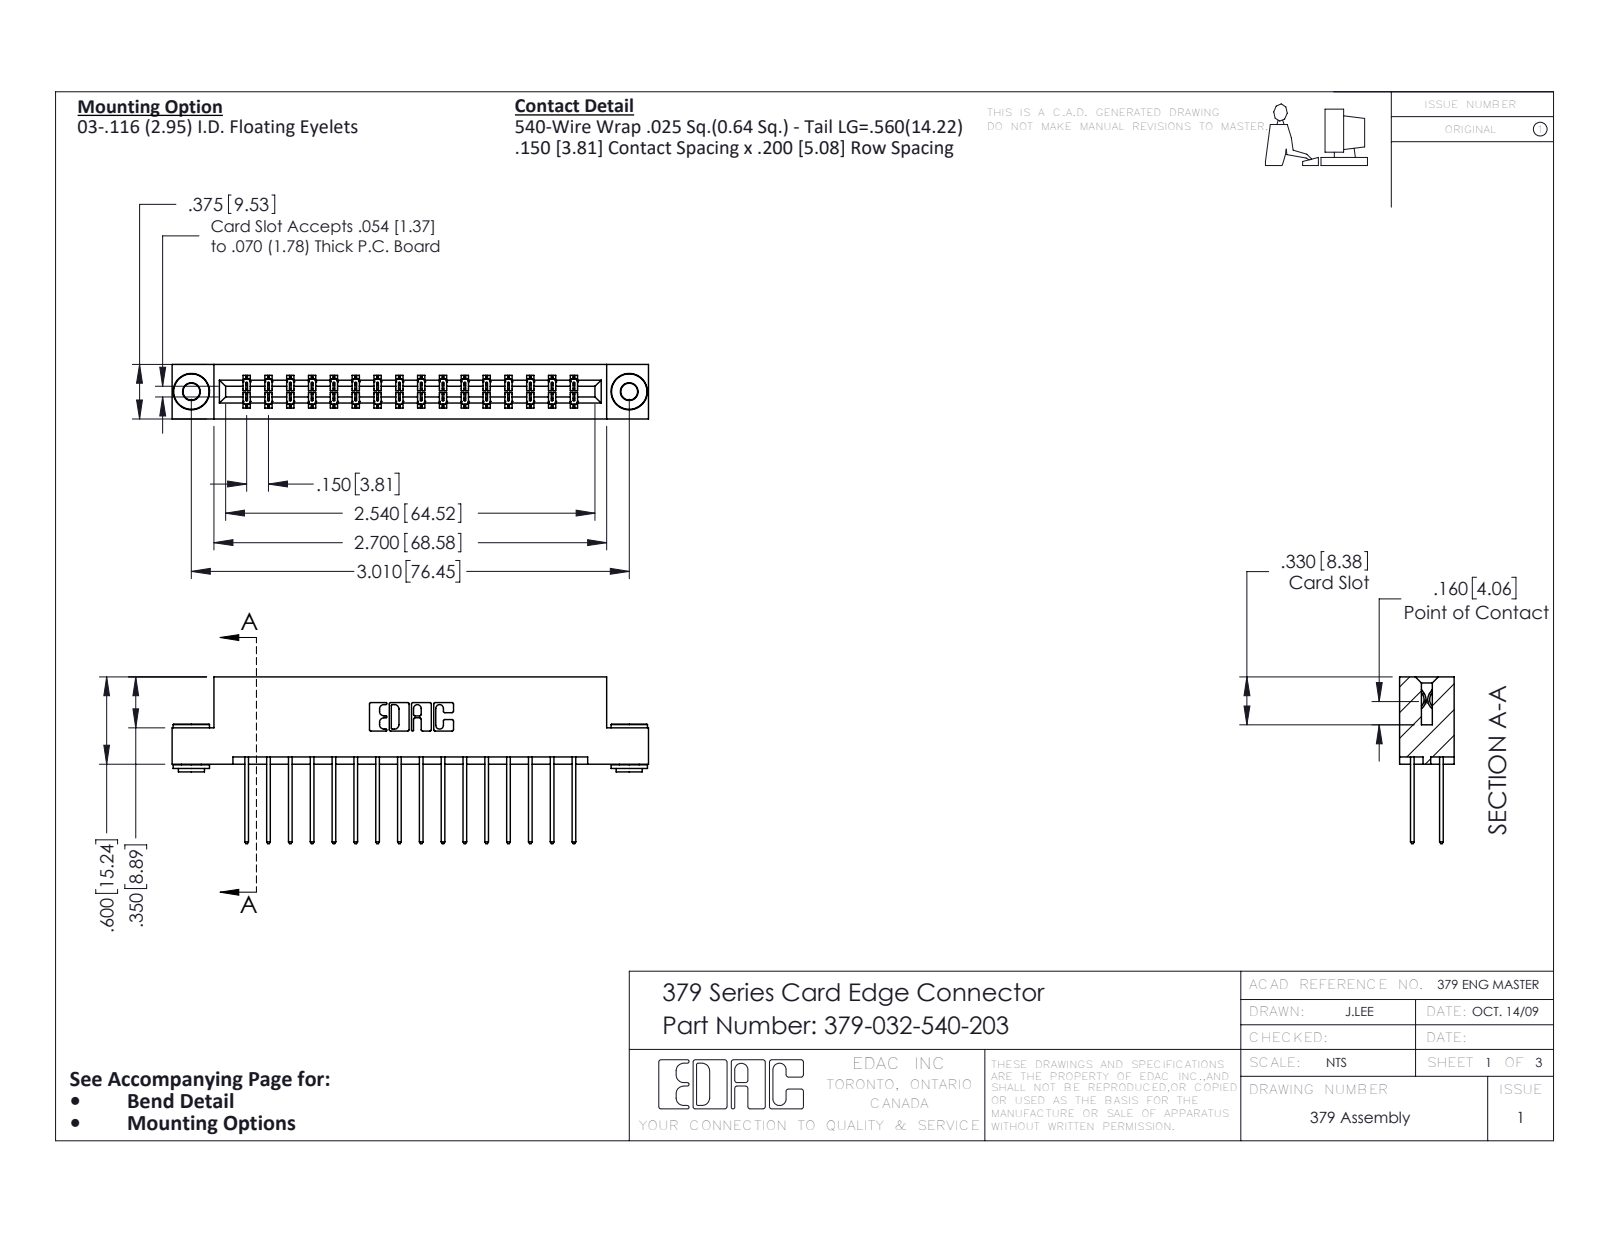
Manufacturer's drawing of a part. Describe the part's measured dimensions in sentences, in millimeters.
The part is named "379-032-540-203; 345-292-001_345-293-140; 345-250-002_345-250-002-102; 379 Part_Flush - .156 Dia - TH". Its 3-D file was written by "SolidWorks 2020 (CONFIG_CONTROL_DESIGN)". It is 35 solids with 1816 faces: 1232 planar, 576 cylindrical and 8 other. Overall it measures 83.2 by 29.1 by 9.5 millimeters. Its volume is 8 670 cubic millimeters and its surface area 10 330 square millimeters. Round holes: 2 of diameter 2.9, 2 of diameter 4. Round bosses or shafts: 2 of diameter 6.4, 2 of diameter 4.6, 2 of diameter 3.5. Partial cylindrical surfaces (rounded edges, fillets, slot ends): 63 of radius 0.2, 32 of radius 0.3, 22 of radius 0.3, 6 of radius 0.2, 6 of radius 0.8, 3 of radius 0.7, 2 of radius 0.4, 2 of radius 0.6. The main face-to-face distances are 7.6, 5.1, 1.9, 2.5, 9.5, 7, 3.8, 1.3, 0.6, 15.2. The hole center spacings are 76.5.
